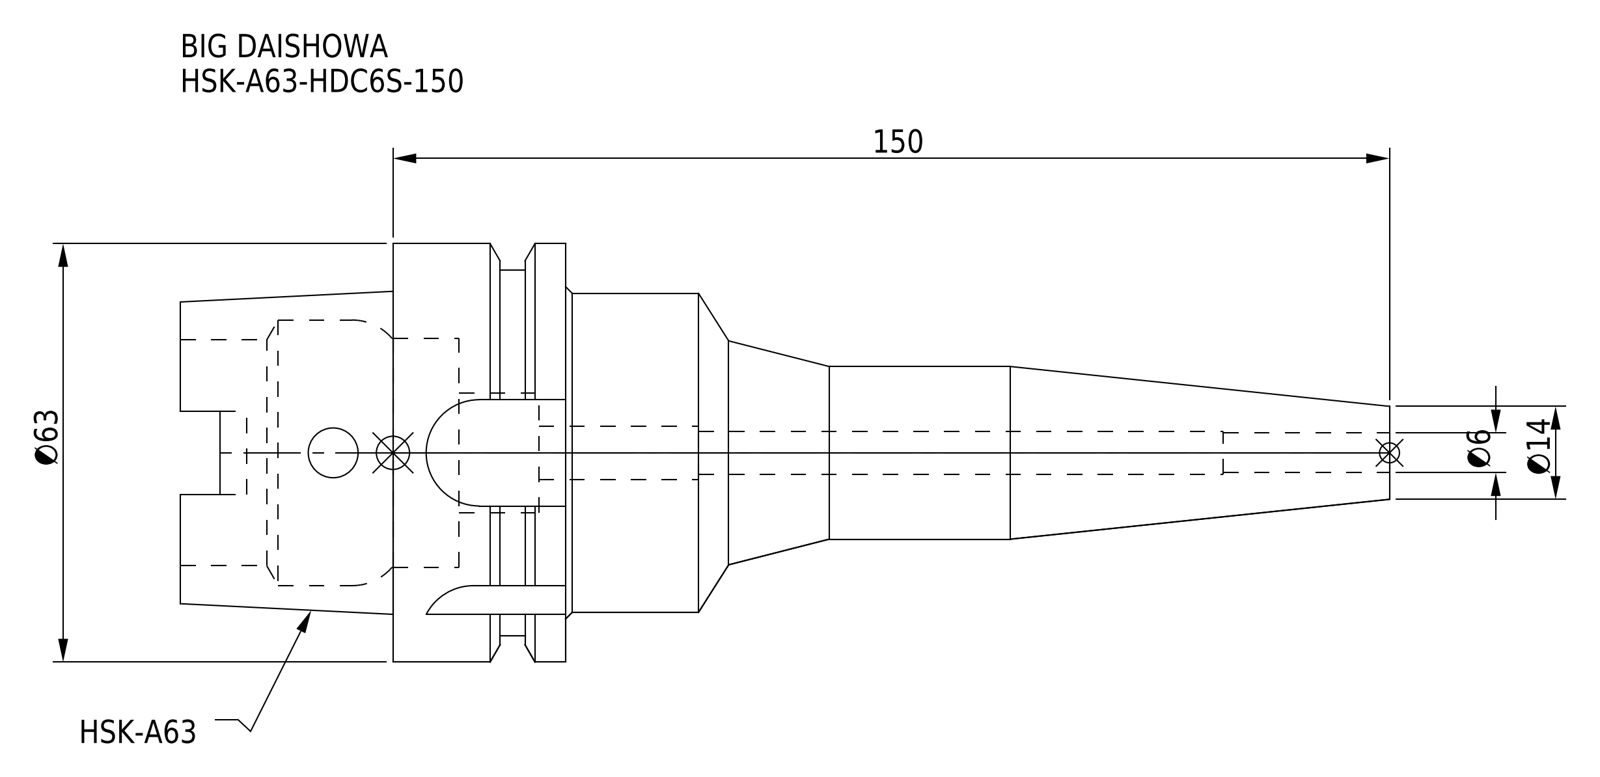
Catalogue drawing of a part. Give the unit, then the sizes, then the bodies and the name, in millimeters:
Units: millimetres
Overall size (bounding box): 182 × 63 × 63
Round holes (diameter × count): ⌀6 ×1, ⌀6.5 ×1, ⌀7.5 ×1, ⌀8 ×1, ⌀18 ×1, ⌀34 ×1, ⌀34.5 ×1, ⌀40 ×1
Round bosses / shafts (diameter × count): ⌀63 ×1, ⌀55 ×1, ⌀48 ×1, ⌀26 ×1
Partial cylindrical surfaces — rounded edges, fillets, slot ends (radius × count): R2.88 ×4, R8 ×4
Main face-to-face distances: 26, 16.05, 9.95, 58, 41.95, 32, 53, 12, 4.05, 21.95
Volume: 163 148 mm³ · Surface area: 34 605 mm²
Bodies: 1 solid, 99 faces (38 planar, 39 cylindrical, 22 other)
Part name (STEP PRODUCT): HSK-A63-HDC6S-150
STEP written by: CREO PARAMETRIC BY PTC INC, 2016380 (AUTOMOTIVE_DESIGN)
